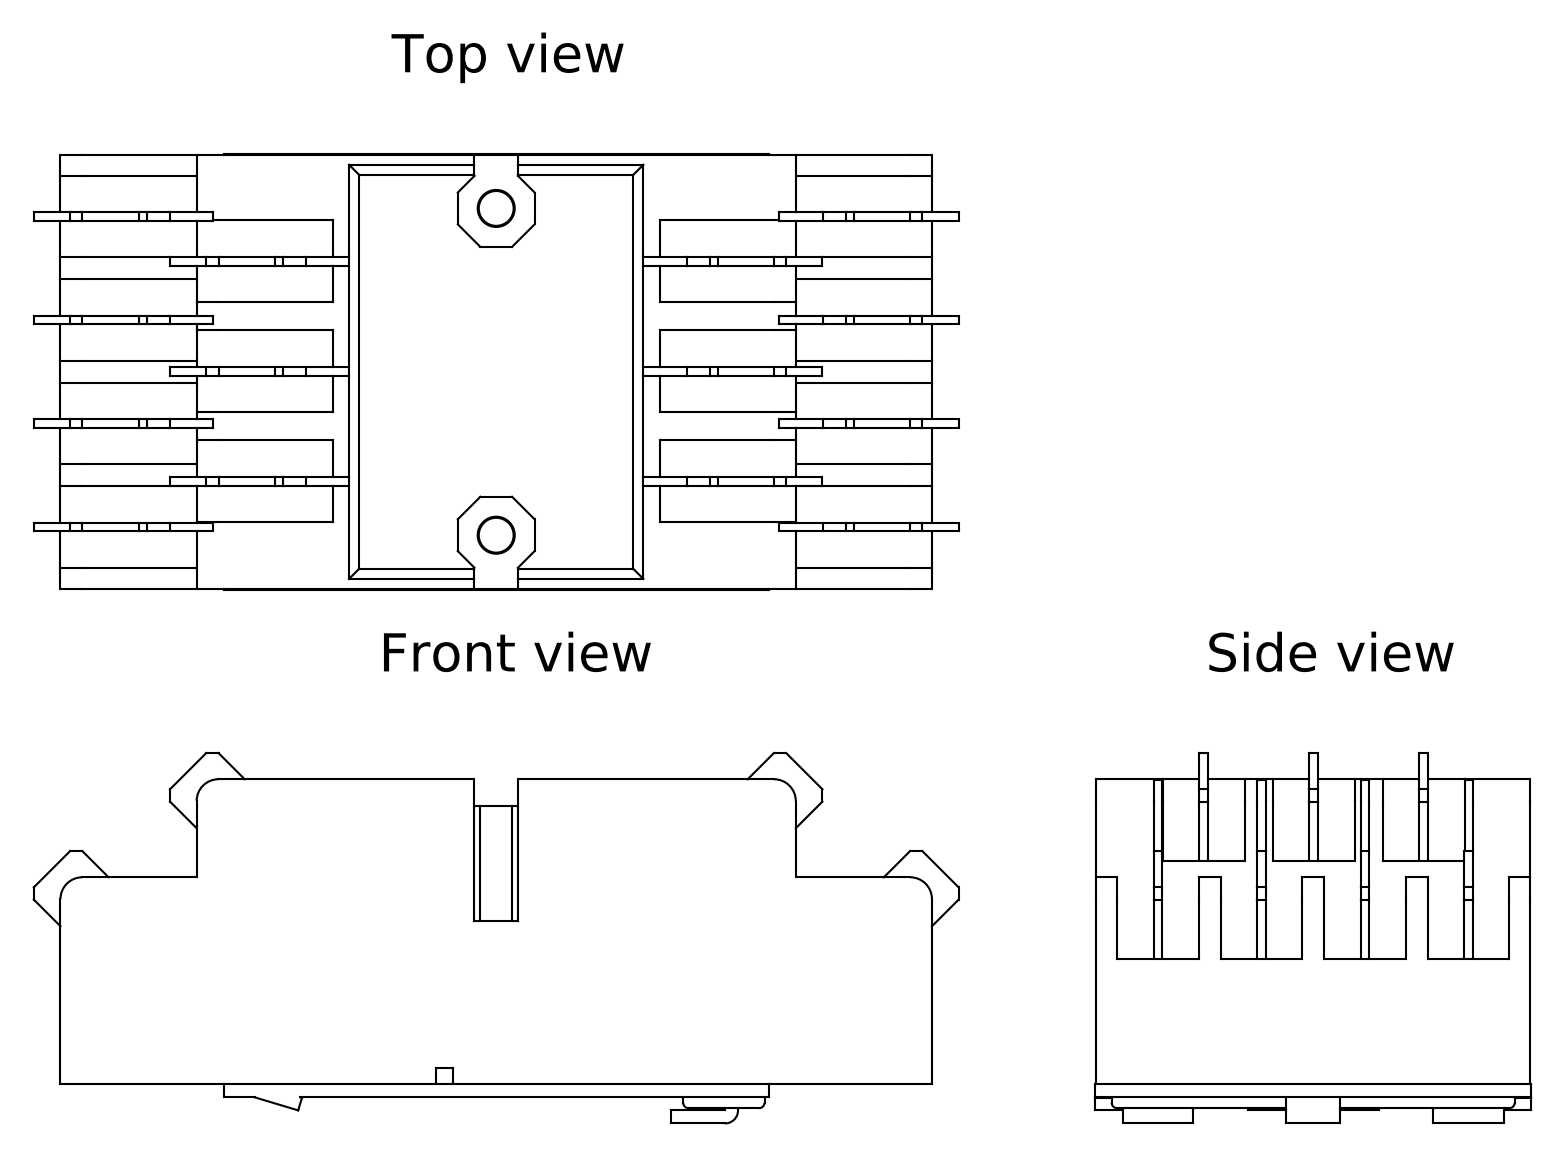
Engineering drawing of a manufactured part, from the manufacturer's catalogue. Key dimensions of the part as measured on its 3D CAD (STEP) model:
Part name (STEP PRODUCT): V25
STEP written by: Autodesk Inventor 2009 (AUTOMOTIVE_DESIGN)
Units: millimetres
Bodies: 1 solid, 584 faces (495 planar, 81 cylindrical, 8 other)
Overall size (bounding box): 84.89 × 40 × 34
Volume: 69 504 mm³ · Surface area: 21 488 mm²
Round holes (diameter × count): ⌀2 ×2
Partial cylindrical surfaces — rounded edges, fillets, slot ends (radius × count): R1 ×14, R0.5 ×10, R2 ×4, R1.2 ×1
Main face-to-face distances: 9.5, 0.8, 39.8, 19, 1.2, 14, 10.1, 12.5, 25.5, 10.3
Hole centre spacings: 2.52
